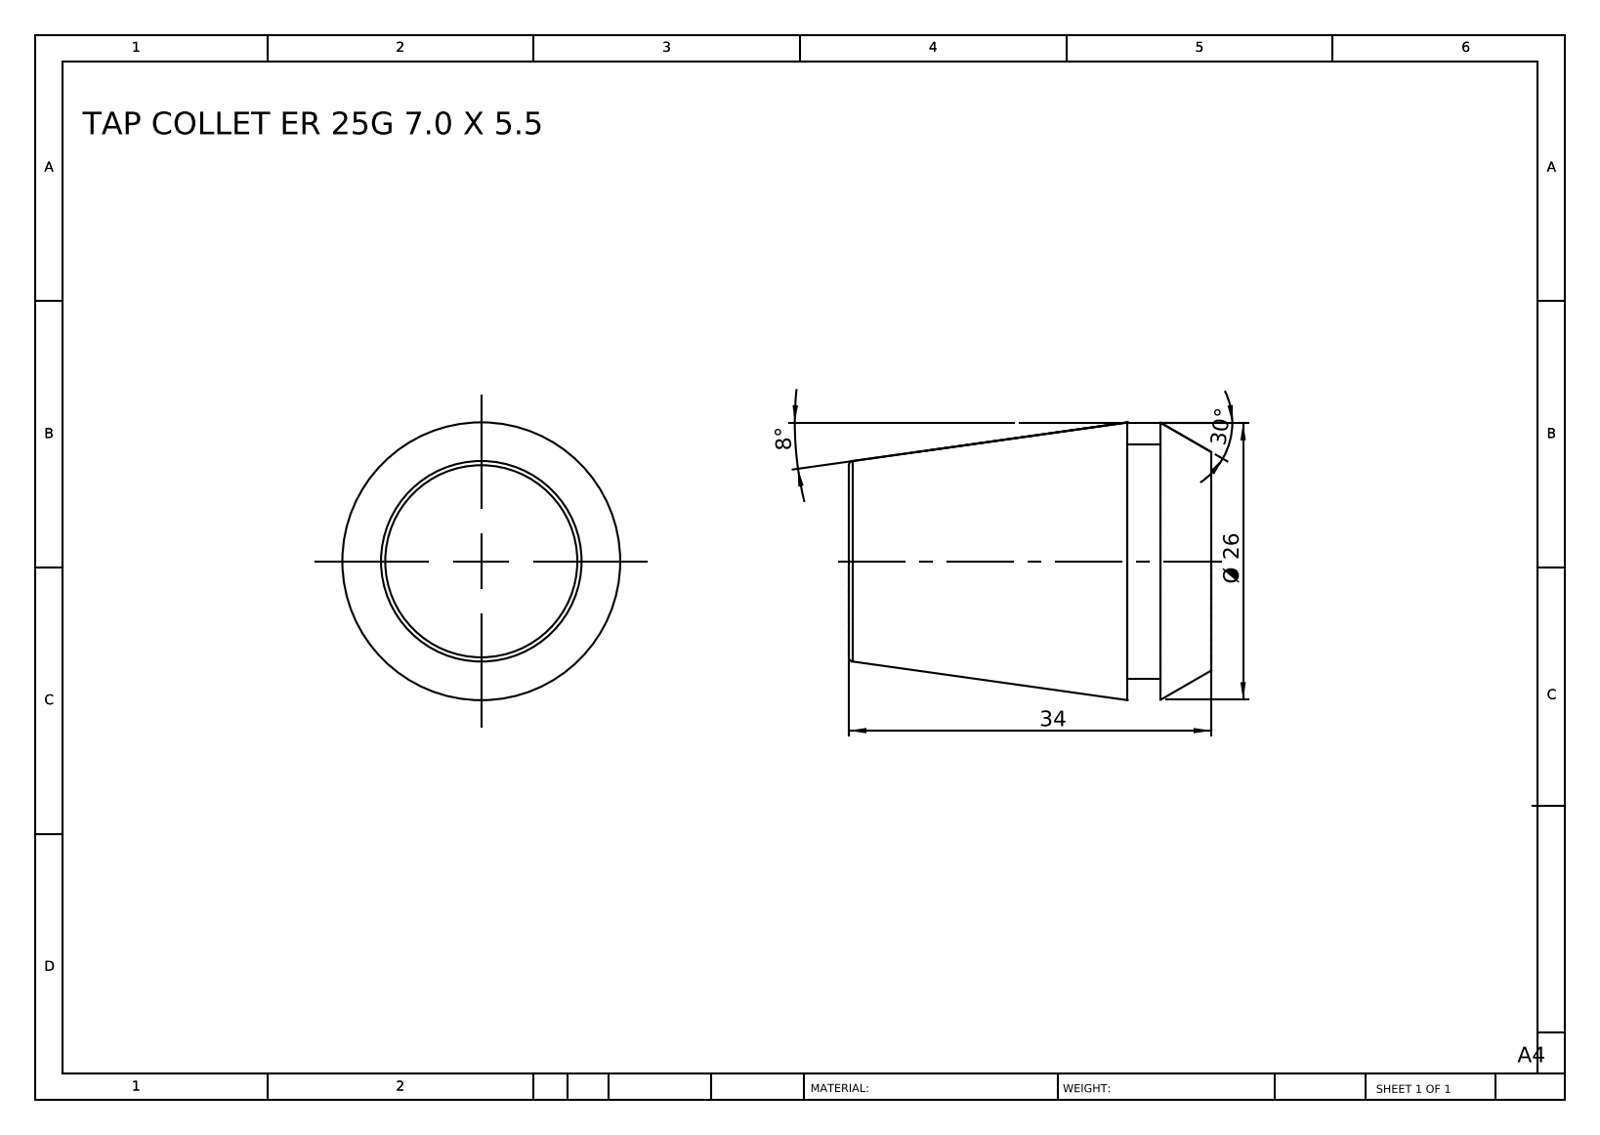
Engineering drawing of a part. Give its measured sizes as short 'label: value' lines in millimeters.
name: TAP COLLET ER 25G 7.0 X 5.5
written by: SolidWorks 2014 (CONFIG_CONTROL_DESIGN)
unit: mm
bodies: 1 solid, 12 faces (4 planar, 2 cylindrical, 6 other)
size: 34 × 26.07 × 26.07
volume: 13 600 mm³; area: 3 376 mm²
bosses: 1× ⌀22
face distances: 34, 7.84, 26.16, 4.74, 3.1, 29.26
